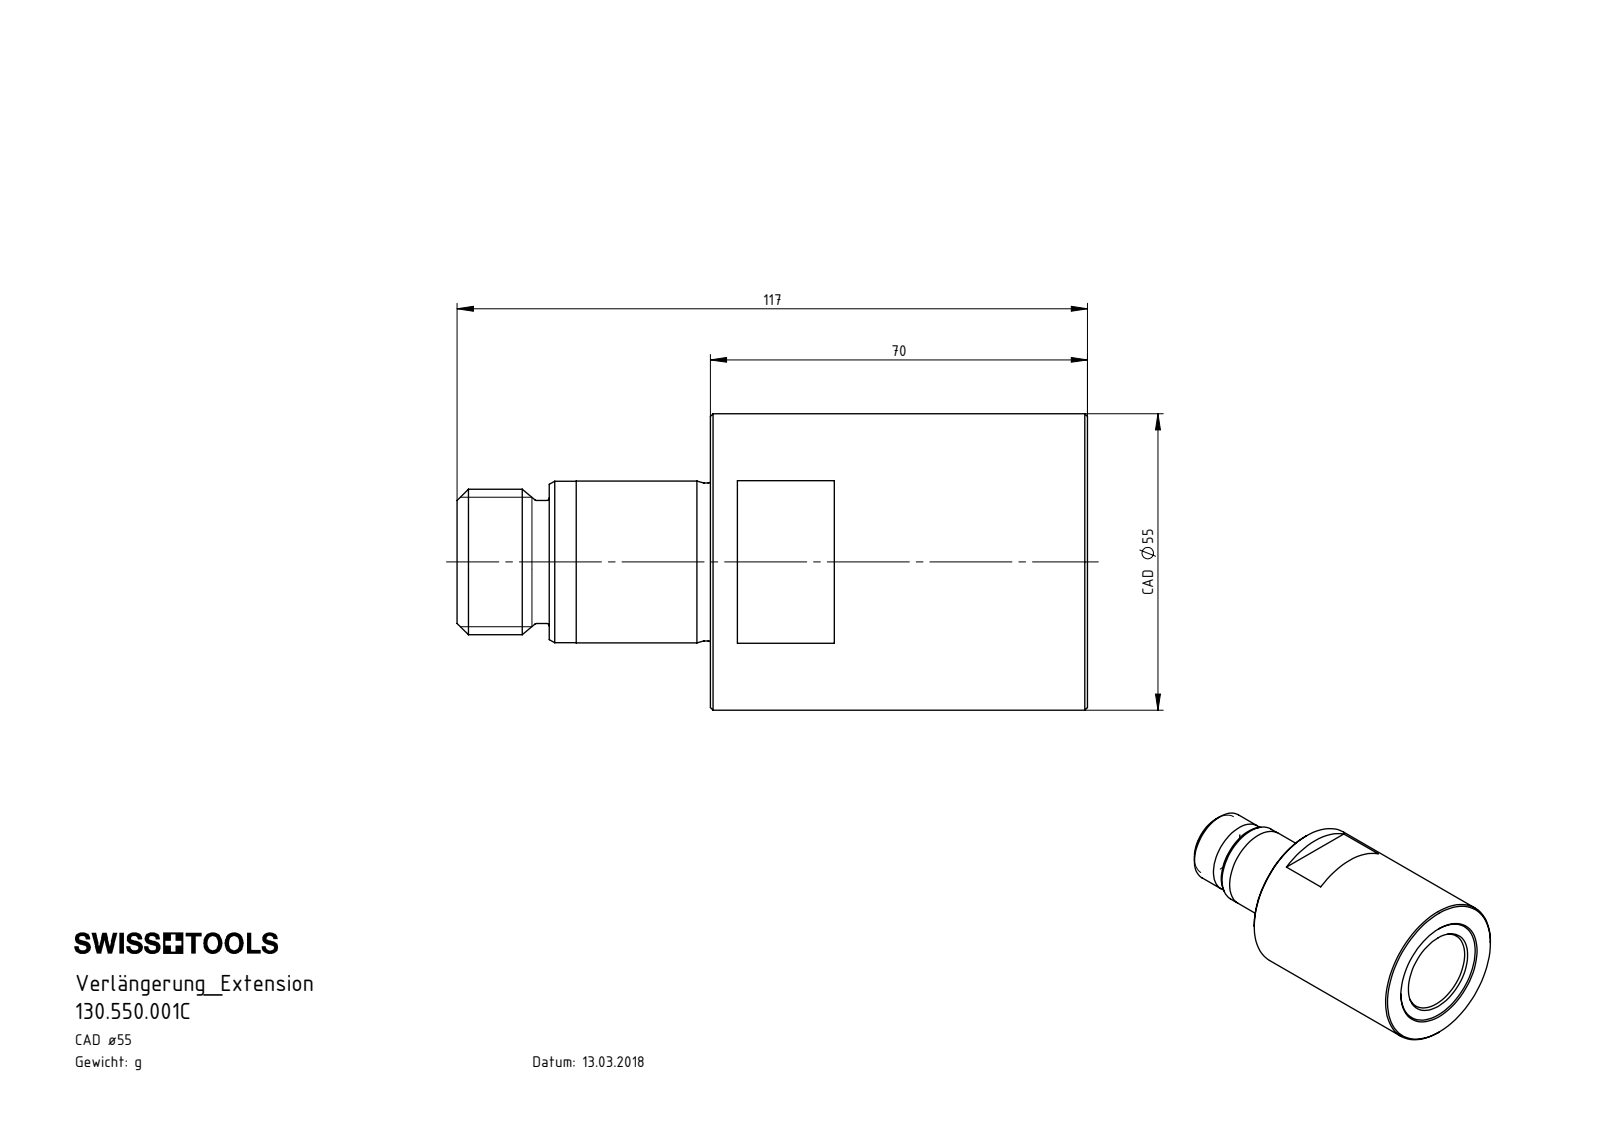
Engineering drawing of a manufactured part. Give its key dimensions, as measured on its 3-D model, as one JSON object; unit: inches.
{"part_name": "130.550.001C", "step_written_by": "SolidWorks 2017 (CONFIG_CONTROL_DESIGN)", "units": "inches", "bodies": {"solids": 1, "faces": 71, "planar": 13, "cylindrical": 20, "other": 38}, "overall_size": [4.606, 2.165, 2.165], "volume_in3": 9.262, "surface_area_in2": 43.22, "round_holes": [[0.335, 1], [0.965, 1], [1.181, 1], [1.205, 1]], "round_bosses_or_shafts": [[2.165, 1], [1.179, 1], [1.154, 1], [1.063, 1], [0.898, 1]], "face_to_face_distances": [2.756, 1.811, 1.85, 2.736, 0.02, 4.587, 4.606, 1.177, 0.673, 3.913]}
